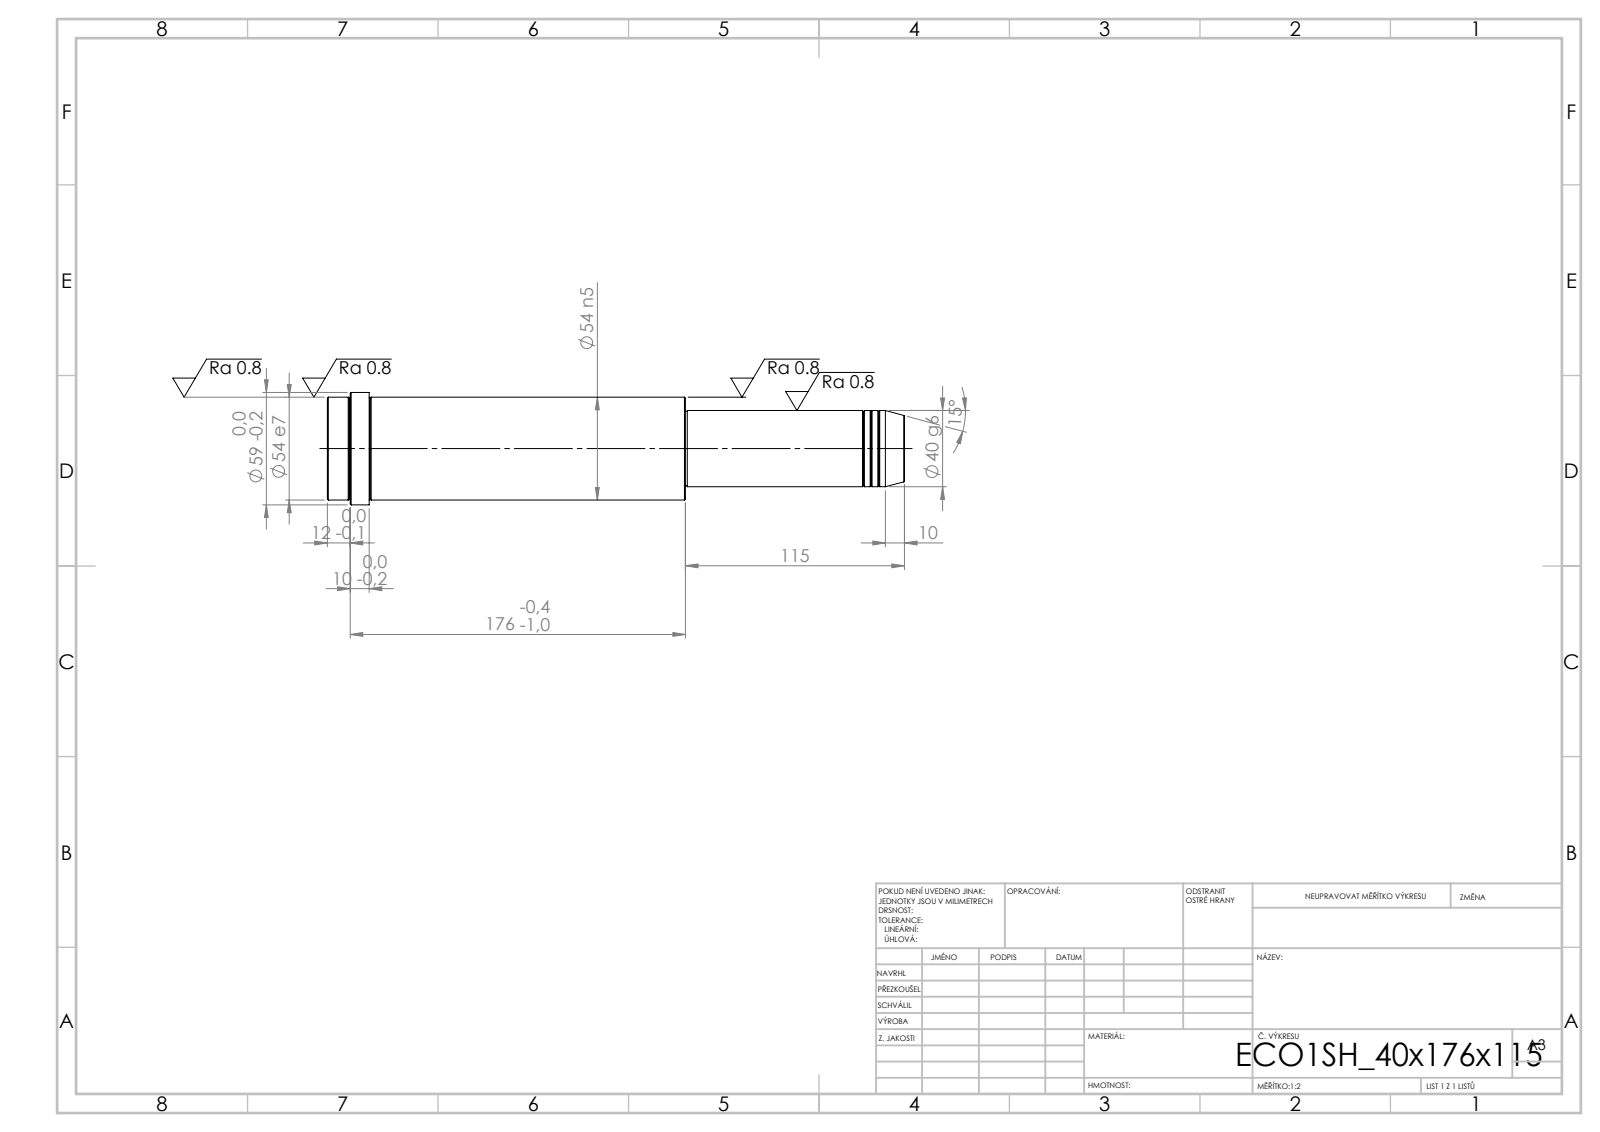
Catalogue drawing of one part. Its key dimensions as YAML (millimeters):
step_written_by: "SolidWorks 2019 (CONFIG_CONTROL_DESIGN)"
units: millimeters
bodies: {solids: 1, faces: 52, planar: 6, cylindrical: 16, other: 30}
overall_size: [303, 59, 59]
volume: 577495
surface_area: 51960
round_bosses_or_shafts:
  - {diameter: 59, count: 1}
  - {diameter: 54, count: 1}
  - {diameter: 40, count: 1}
  - {diameter: 39, count: 1}
face_to_face_distances: [188, 115, 303, 281, 166, 22, 291, 176, 10, 12]
